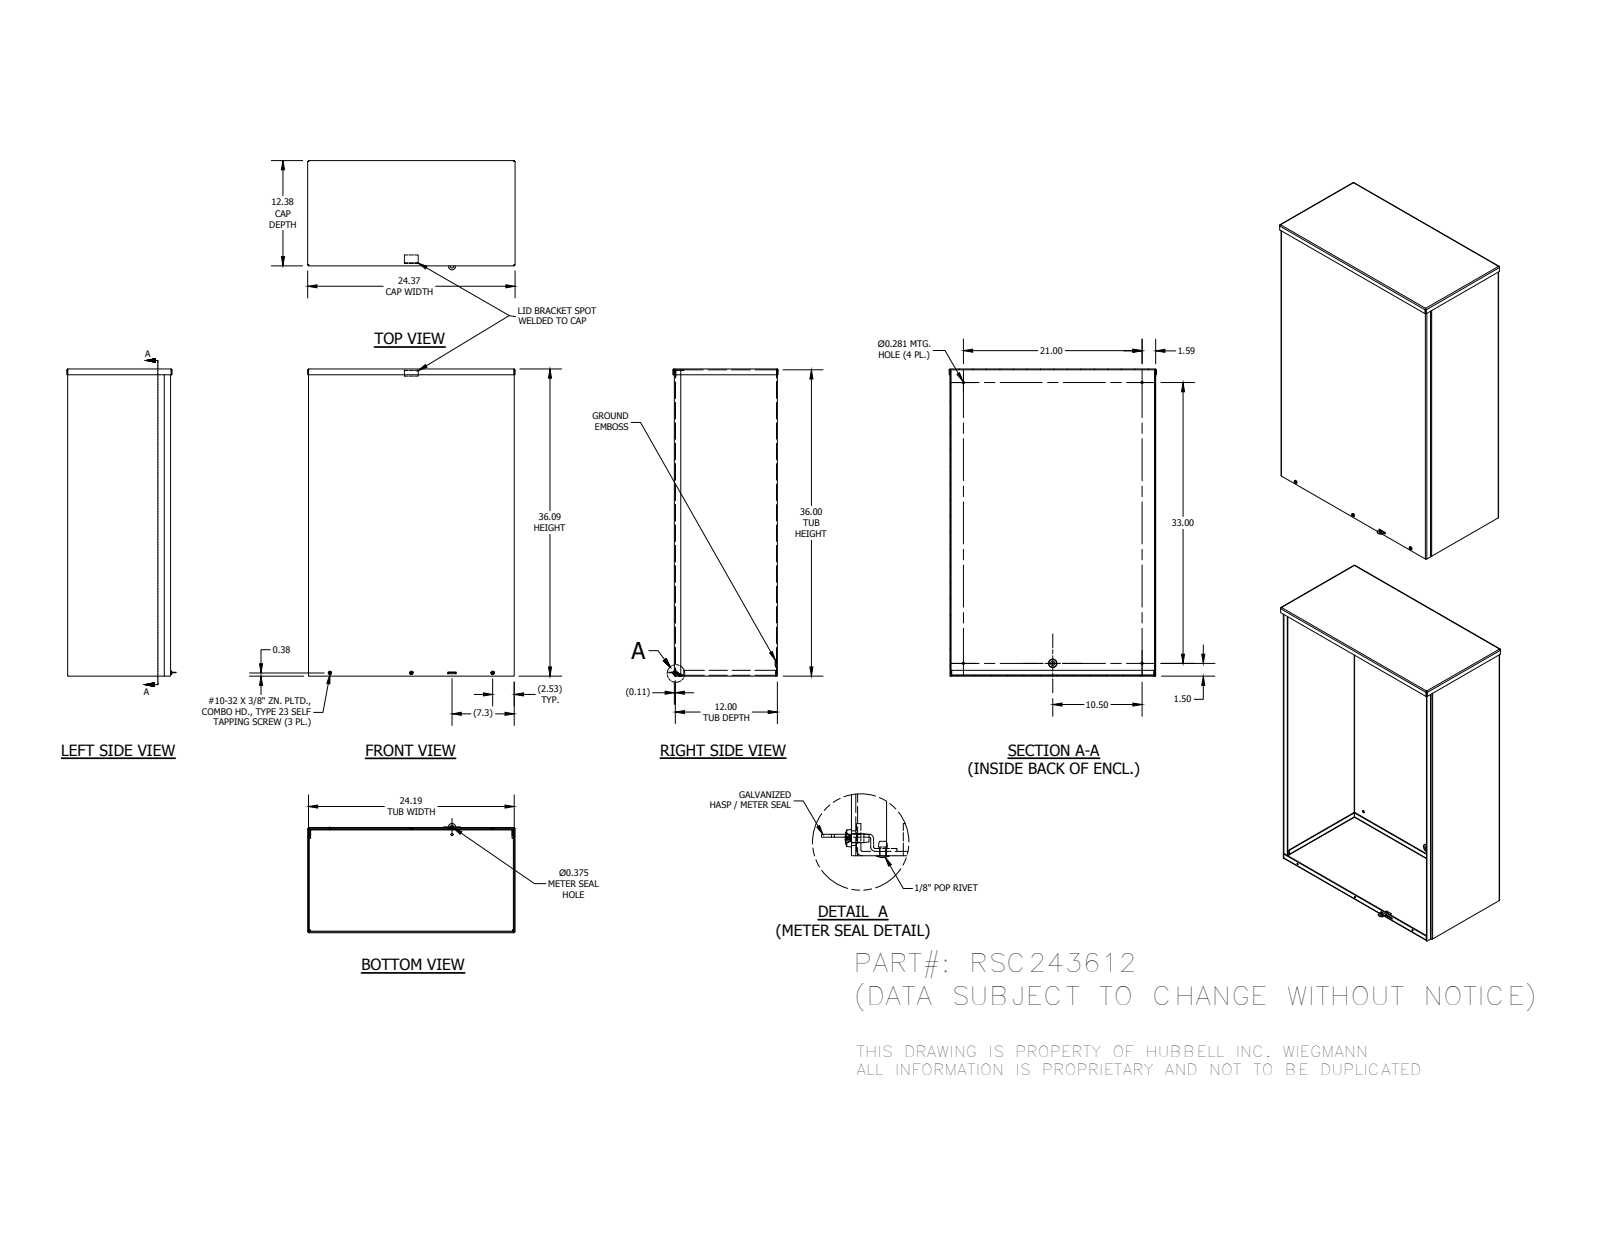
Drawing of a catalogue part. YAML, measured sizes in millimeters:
part_name: "RSC243612BKPA; RSC2412EWPA-12GA; RSC2436LFA; RSC2412CPA-12GA (+5 more)"
step_written_by: "Autodesk Inventor 2014 (AUTOMOTIVE_DESIGN)"
units: millimeters
bodies: {solids: 10, faces: 353, planar: 214, cylindrical: 62, other: 77}
overall_size: [917.8, 619.12, 326.24]
volume: 5086000
surface_area: 4304000
round_holes:
  - {diameter: 7.94, count: 6}
  - {diameter: 4.34, count: 4}
  - {diameter: 7.14, count: 4}
  - {diameter: 3.17, count: 1}
  - {diameter: 3.45, count: 1}
  - {diameter: 9.52, count: 1}
round_bosses_or_shafts:
  - {diameter: 4.83, count: 3}
  - {diameter: 6.65, count: 1}
  - {diameter: 3.17, count: 1}
partial_cylinders:
  - {radius: 0.79, count: 19}
  - {radius: 3.17, count: 16}
  - {radius: 2.37, count: 2}
  - {radius: 2.67, count: 1}
  - {radius: 10.16, count: 1}
face_to_face_distances: [2.38, 305.2, 307.58, 302.82, 611.98, 914.4, 614.36, 609.6, 916.78, 912.02]
hole_center_spacings: [242.89, 268.23, 510.39, 927.71, 895.35, 37.19, 37.2, 244.56]
